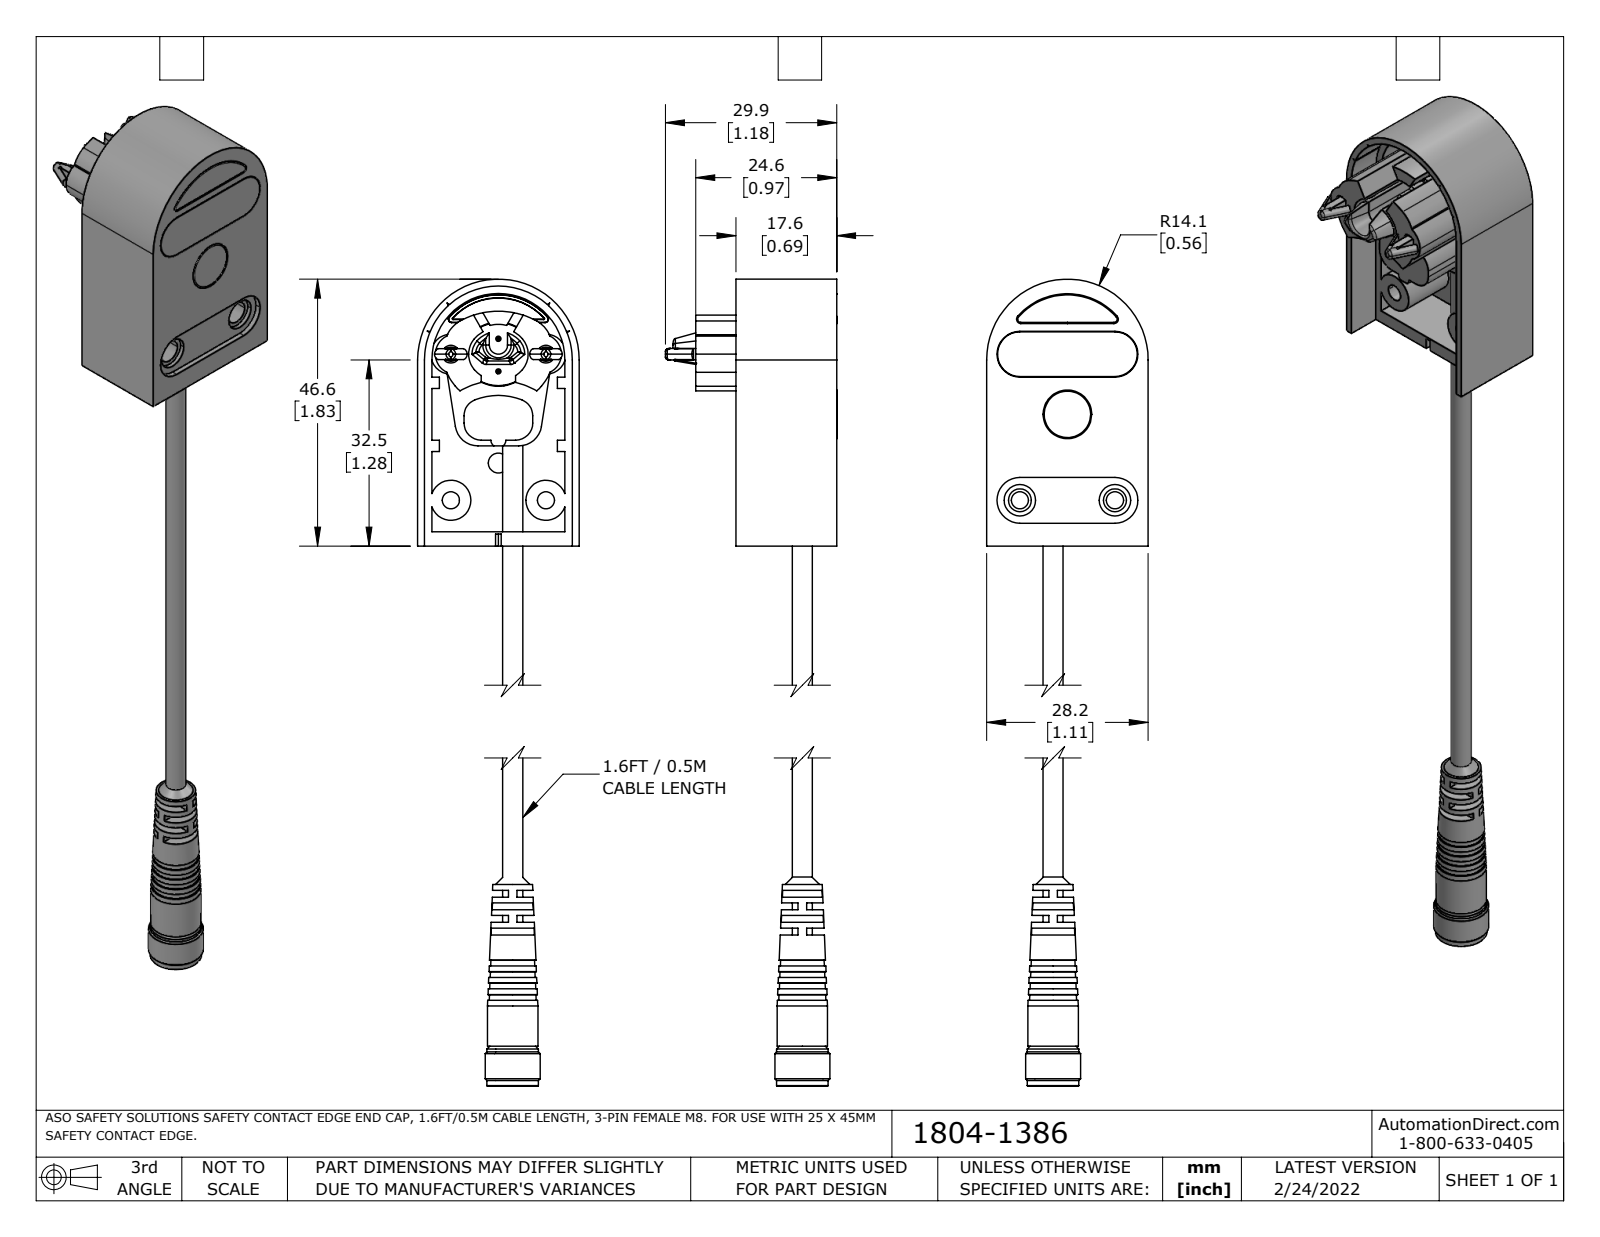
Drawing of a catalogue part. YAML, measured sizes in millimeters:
part_name: "1804-1386_Default"
step_written_by: "SolidWorks 2021 (CONFIG_CONTROL_DESIGN)"
units: millimeters
bodies: {solids: 11, faces: 724, planar: 248, cylindrical: 304, other: 172}
overall_size: [172.5, 30, 28.2]
volume: 14700
surface_area: 16700
round_holes:
  - {diameter: 0.5, count: 4}
  - {diameter: 4, count: 4}
  - {diameter: 5.5, count: 4}
  - {diameter: 0.8, count: 3}
  - {diameter: 0.8, count: 3}
  - {diameter: 1.6, count: 3}
  - {diameter: 3.5, count: 3}
  - {diameter: 3, count: 2}
  - {diameter: 3.1, count: 2}
  - {diameter: 3.4, count: 1}
  - {diameter: 5.9, count: 1}
  - {diameter: 6.9, count: 1}
round_bosses_or_shafts:
  - {diameter: 1.2, count: 13}
  - {diameter: 0.5, count: 6}
  - {diameter: 3.5, count: 3}
  - {diameter: 1, count: 3}
  - {diameter: 7, count: 2}
  - {diameter: 5, count: 2}
  - {diameter: 2.5, count: 2}
  - {diameter: 2, count: 2}
partial_cylinders:
  - {radius: 1, count: 12}
  - {radius: 0.1, count: 9}
  - {radius: 0.3, count: 6}
  - {radius: 3, count: 6}
  - {radius: 3.5, count: 6}
  - {radius: 4, count: 6}
  - {radius: 0.5, count: 5}
  - {radius: 5, count: 4}
face_to_face_distances: [1.8, 2.5, 1, 28.2, 1.3, 1.2, 27, 25.7, 0.8, 24.5]
hole_center_spacings: [16.6, 1.4, 1.8, 2.5, 8.7, 8.8, 10.5, 20.7]
